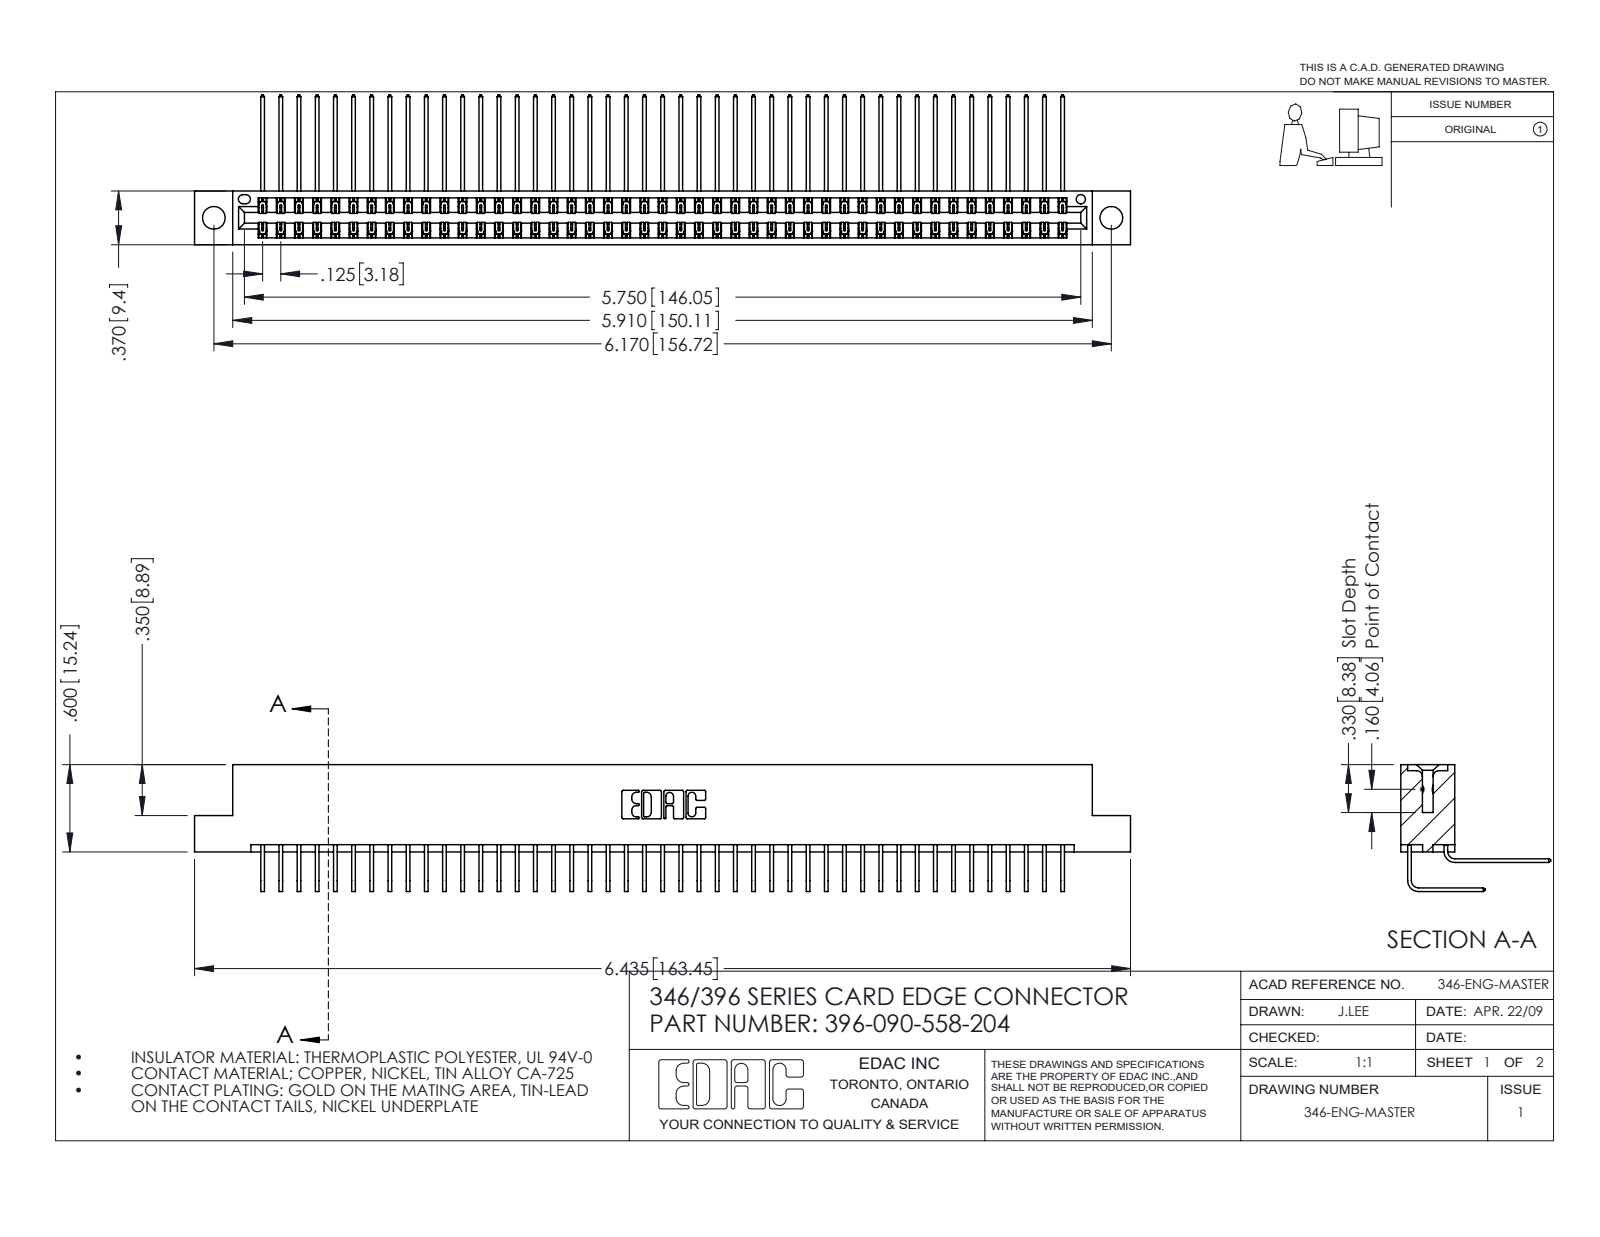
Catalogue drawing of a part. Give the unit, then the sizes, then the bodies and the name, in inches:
Units: inches
Overall size (bounding box): 6.435 × 1.03 × 0.873
Round holes (diameter × count): ⌀0.156 ×2, ⌀0.064 ×1
Partial cylindrical surfaces — rounded edges, fillets, slot ends (radius × count): R0.006 ×135, R0.01 ×22, R0.007 ×6, R0.031 ×6, R0.026 ×3, R0.014 ×2, R0.022 ×2, R0.024 ×2
Main face-to-face distances: 0.322, 0.048, 0.025, 0.37, 0.25, 0.298, 0.072, 0.275, 0.148, 0.222
Hole centre spacings: 0.246, 5.961, 6.17
Volume: 1 in³ · Surface area: 38.57 in²
Bodies: 91 solids, 4982 faces (3406 planar, 1576 cylindrical, 0 other)
Part name (STEP PRODUCT): 346 Part_Flush Mounting Lugs - 0.156 Dia-TH; 345-292-001_558 Tail - 2; 345-292-001_558 559 Tail - 1; 396-090-558-204
STEP written by: SolidWorks 2016 (CONFIG_CONTROL_DESIGN)
